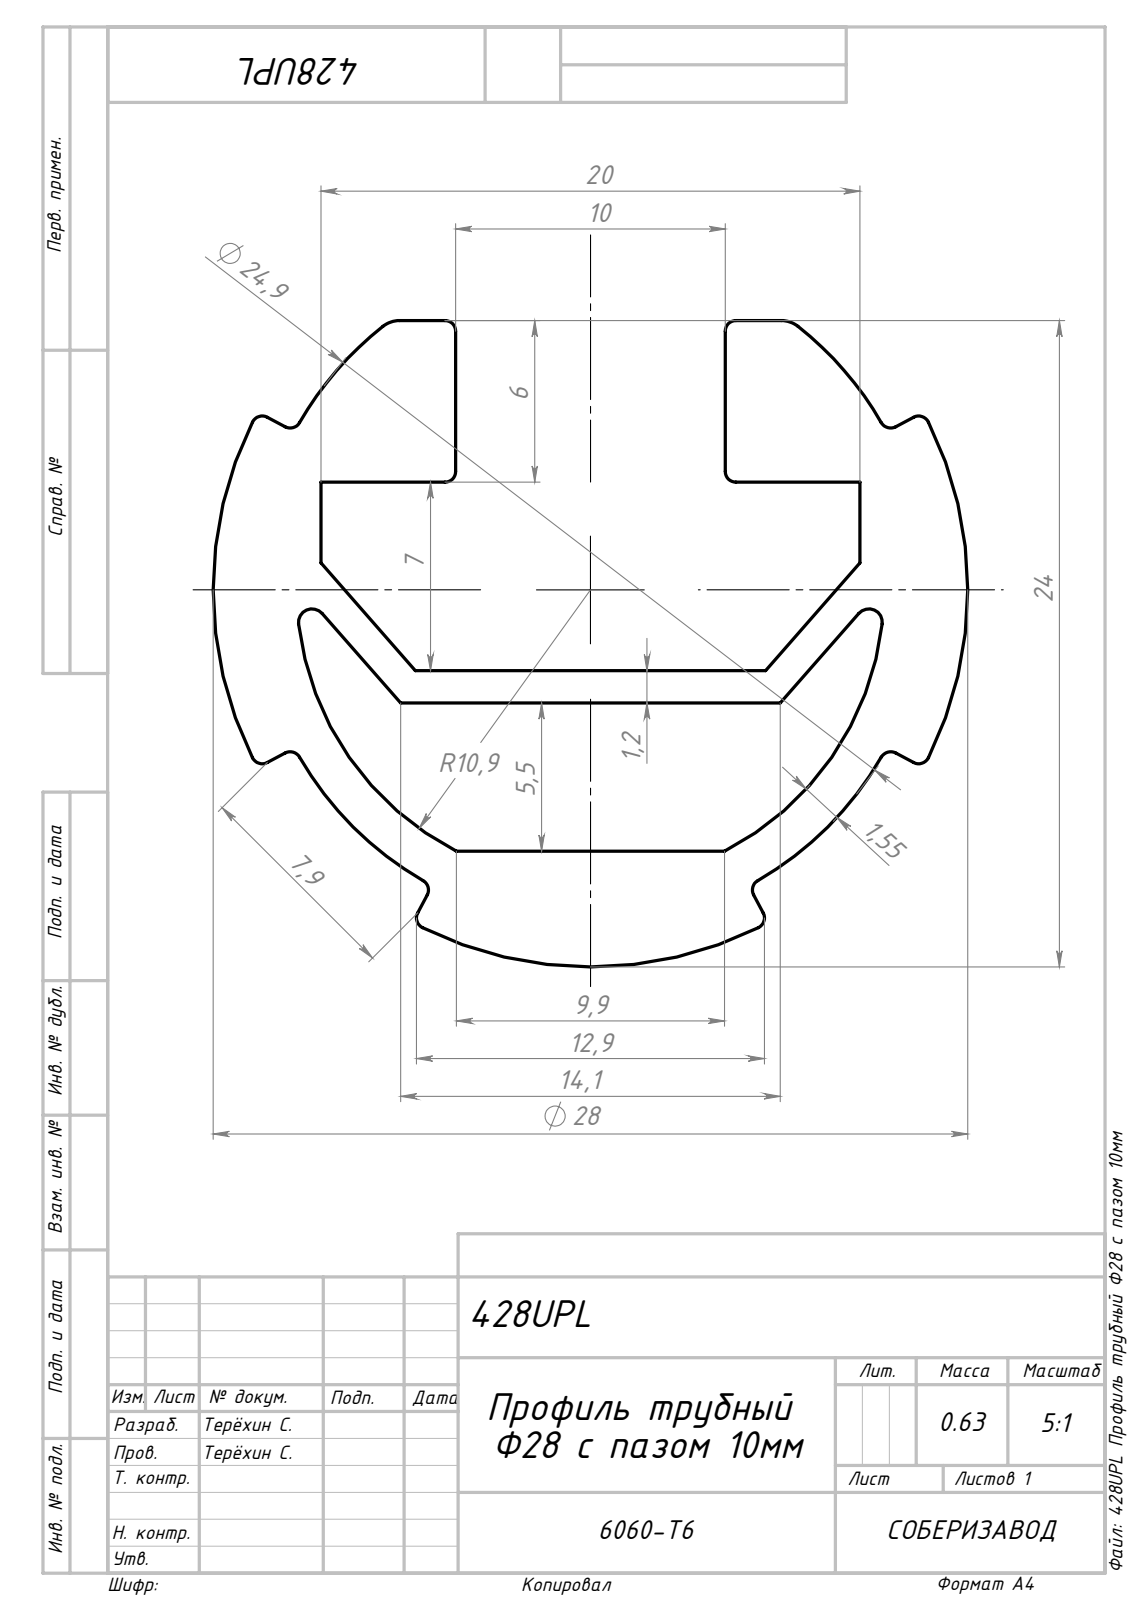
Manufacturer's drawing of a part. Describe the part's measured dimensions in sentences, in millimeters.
The part is named "428UPL Профиль трубный Φ28 с пазом 10мм". Its 3-D file was written by "SolidWorks 2022 (AUTOMOTIVE_DESIGN)". It is 1 solid with 56 faces: 23 planar, 33 cylindrical and 0 other. Overall it measures 1000 by 28 by 24 millimeters. Its volume is 233 260 cubic millimeters and its surface area 187 132 square millimeters. Partial cylindrical surfaces (rounded edges, fillets, slot ends): 16 of radius 0.4, 2 of radius 0.5, 2 of radius 1, 1 of radius 10.9, 1 of radius 12.45, 1 of radius 14. The main face-to-face distances are 1.2, 5.5, 6.7, 13.7, 8.2, 7, 5, 15, 10, 19.7.
